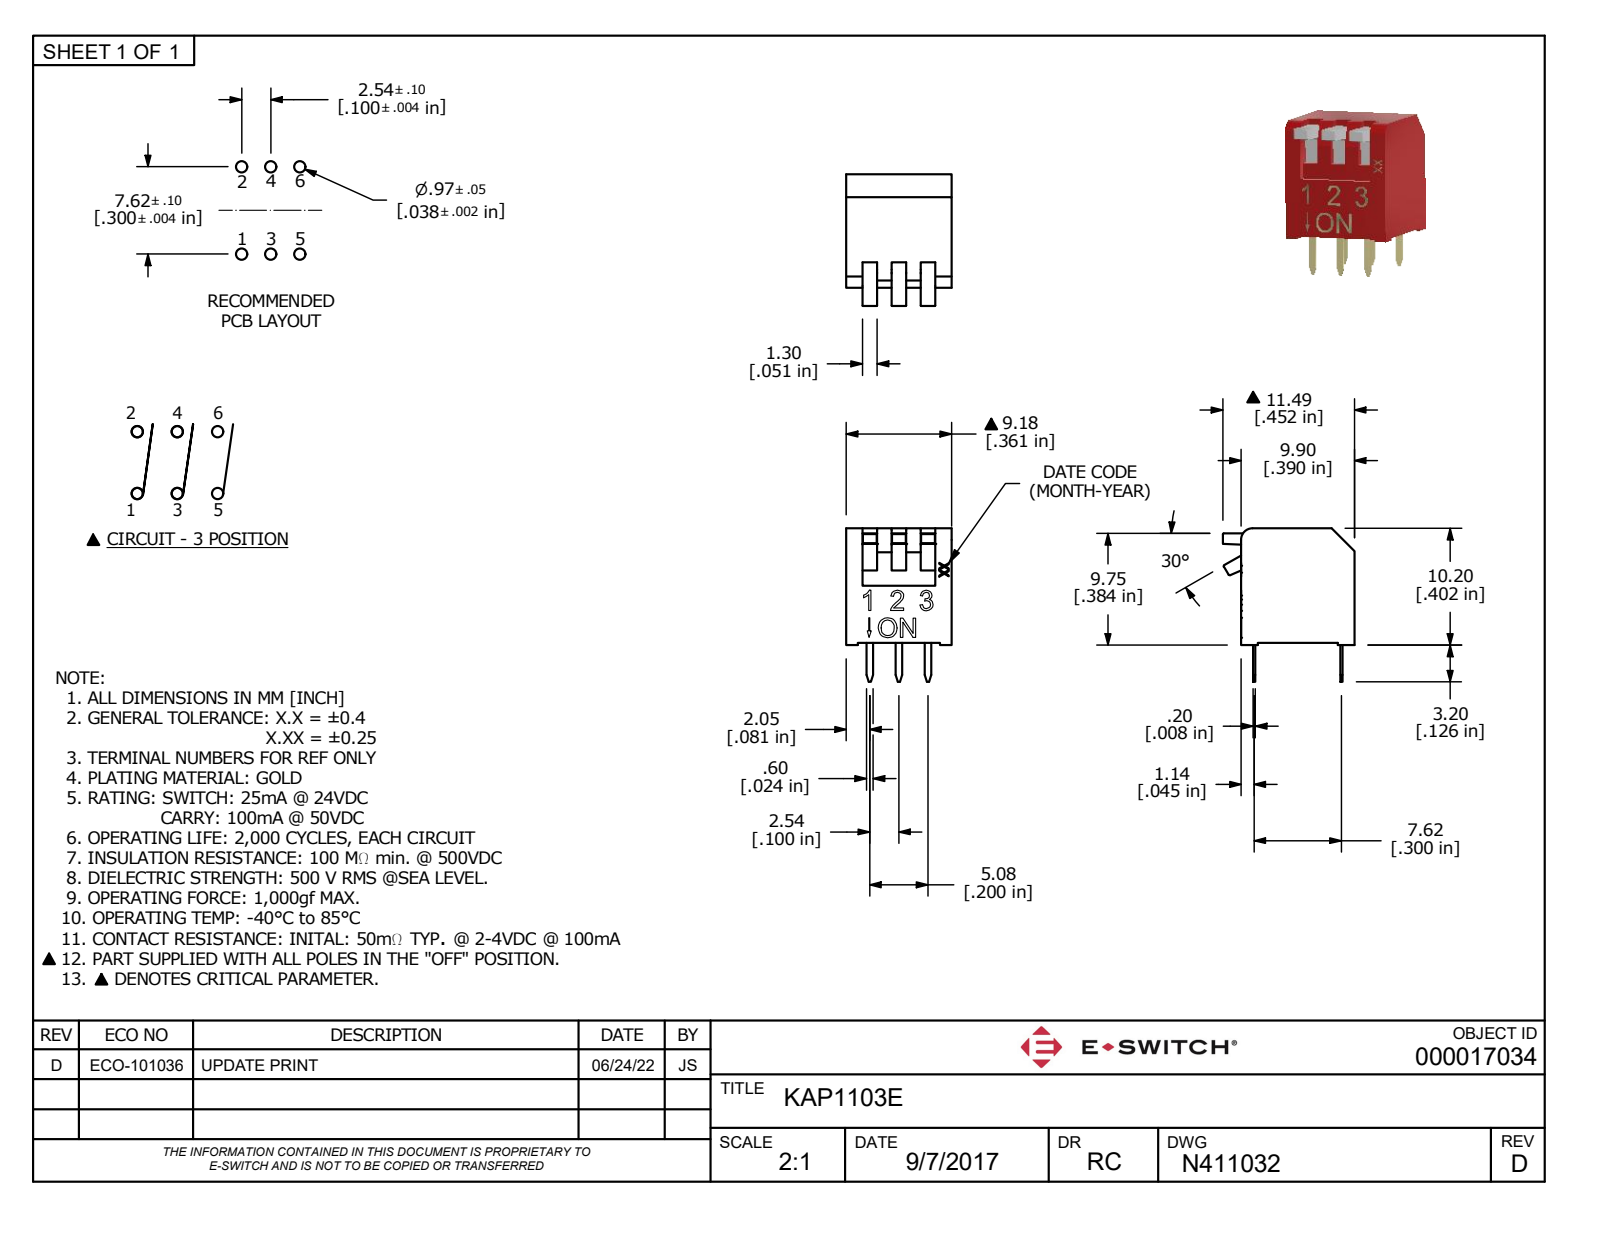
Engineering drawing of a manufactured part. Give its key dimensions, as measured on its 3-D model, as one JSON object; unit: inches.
{"part_name": "P:\\\\E-Switch Secure\\\\3D_MODELS_STP_FORMAT\\\\KAP1103E.stp", "step_written_by": "ACIS (CONFIG_CONTROL_DESIGN)", "units": "inches", "bodies": {"solids": 7, "faces": 228, "planar": 185, "cylindrical": 10, "other": 33}, "overall_size": [0.535, 0.496, 0.361], "volume_in3": 0.056, "surface_area_in2": 1.087, "partial_cylinders_radius": [[0.01, 2], [0.039, 1], [0.269, 1]], "face_to_face_distances": [0.361, 0.394, 0.425, 0.035, 0.327, 0.1, 0.051, 0.139, 0.055, 0.306]}
